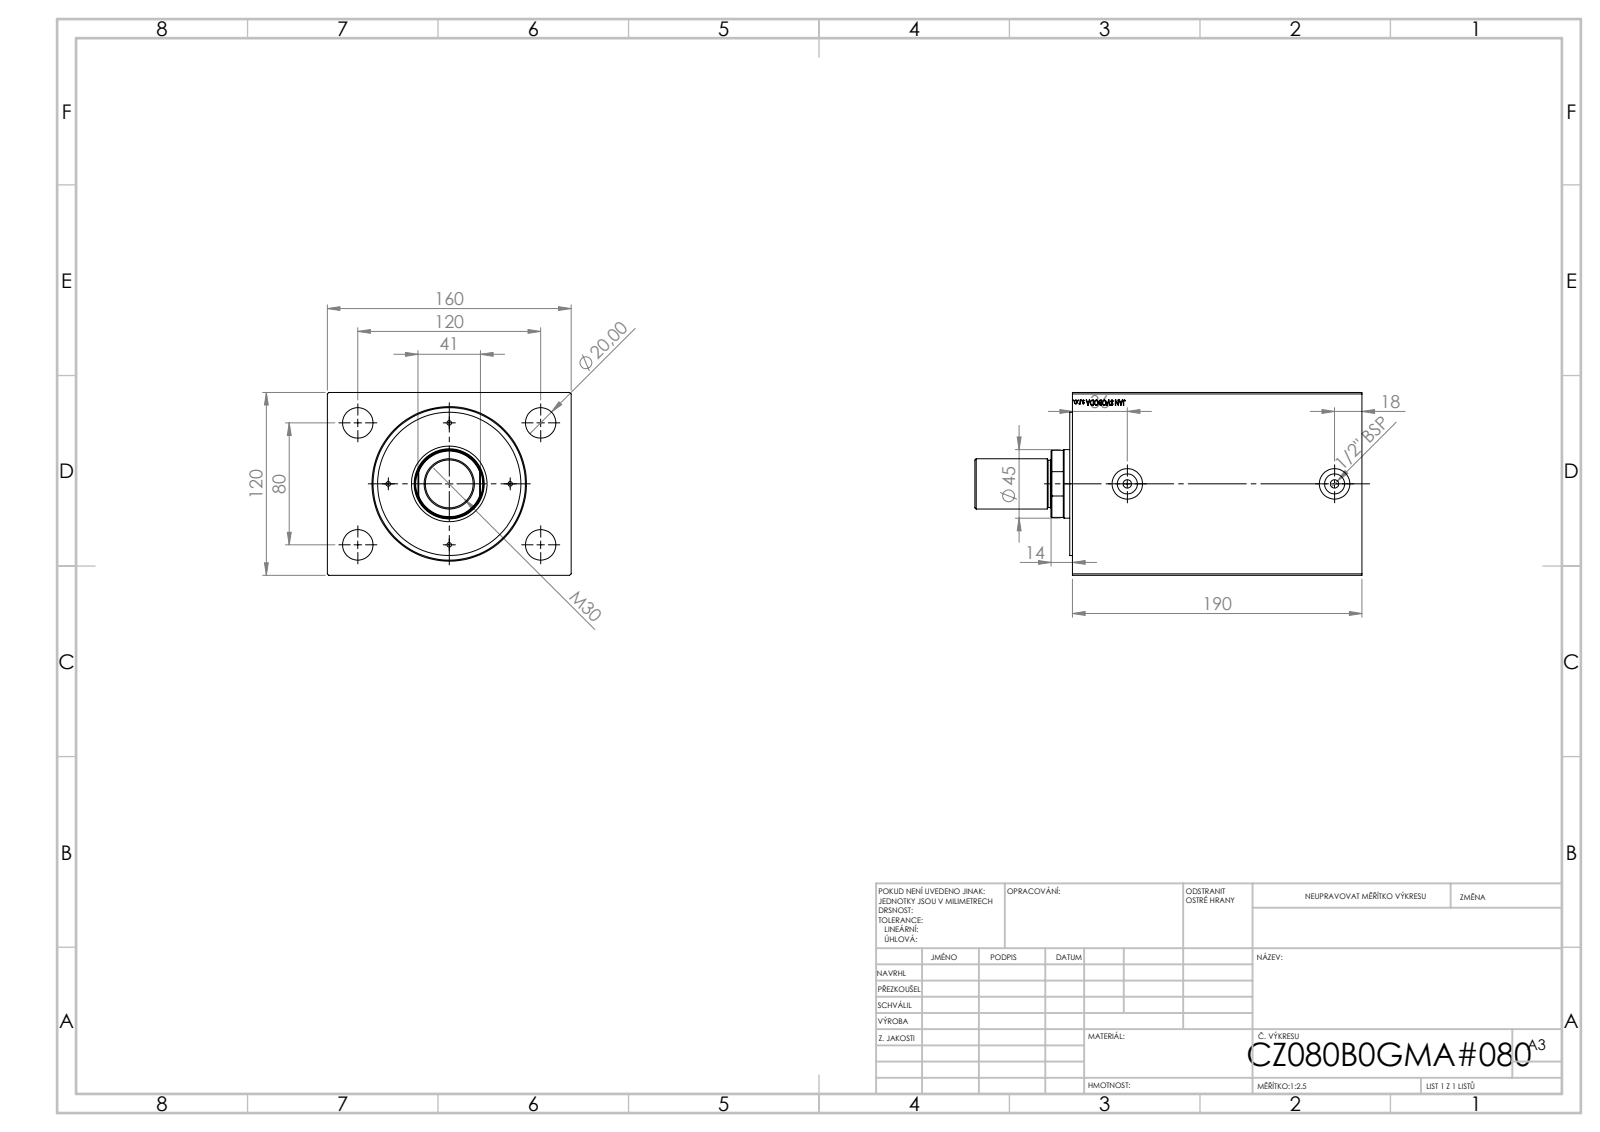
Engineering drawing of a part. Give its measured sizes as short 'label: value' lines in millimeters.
name: V500CZ; V500CZ_MALE_METRIC; V500CZ_B_VC
written by: SolidWorks 2019 (CONFIG_CONTROL_DESIGN)
unit: mm
bodies: 4 solids, 887 faces (403 planar, 62 cylindrical, 422 other)
size: 254 × 160 × 120
volume: 3 568 000 mm³; area: 321 705 mm²
holes: 6× ⌀20, 4× ⌀3, 2× ⌀5.5, 2× ⌀13.16, 1× ⌀28.5, 1× ⌀36, 1× ⌀45, 1× ⌀46, 1× ⌀80, 1× ⌀100
bosses: 1× ⌀94, 1× ⌀33, 1× ⌀31
rounds: 1× R22
face distances: 120, 160, 190, 166, 24, 110, 56, 80, 14, 124
hole spacings: 40, 44.72, 56.57, 60, 72.11, 80, 100, 107.7
